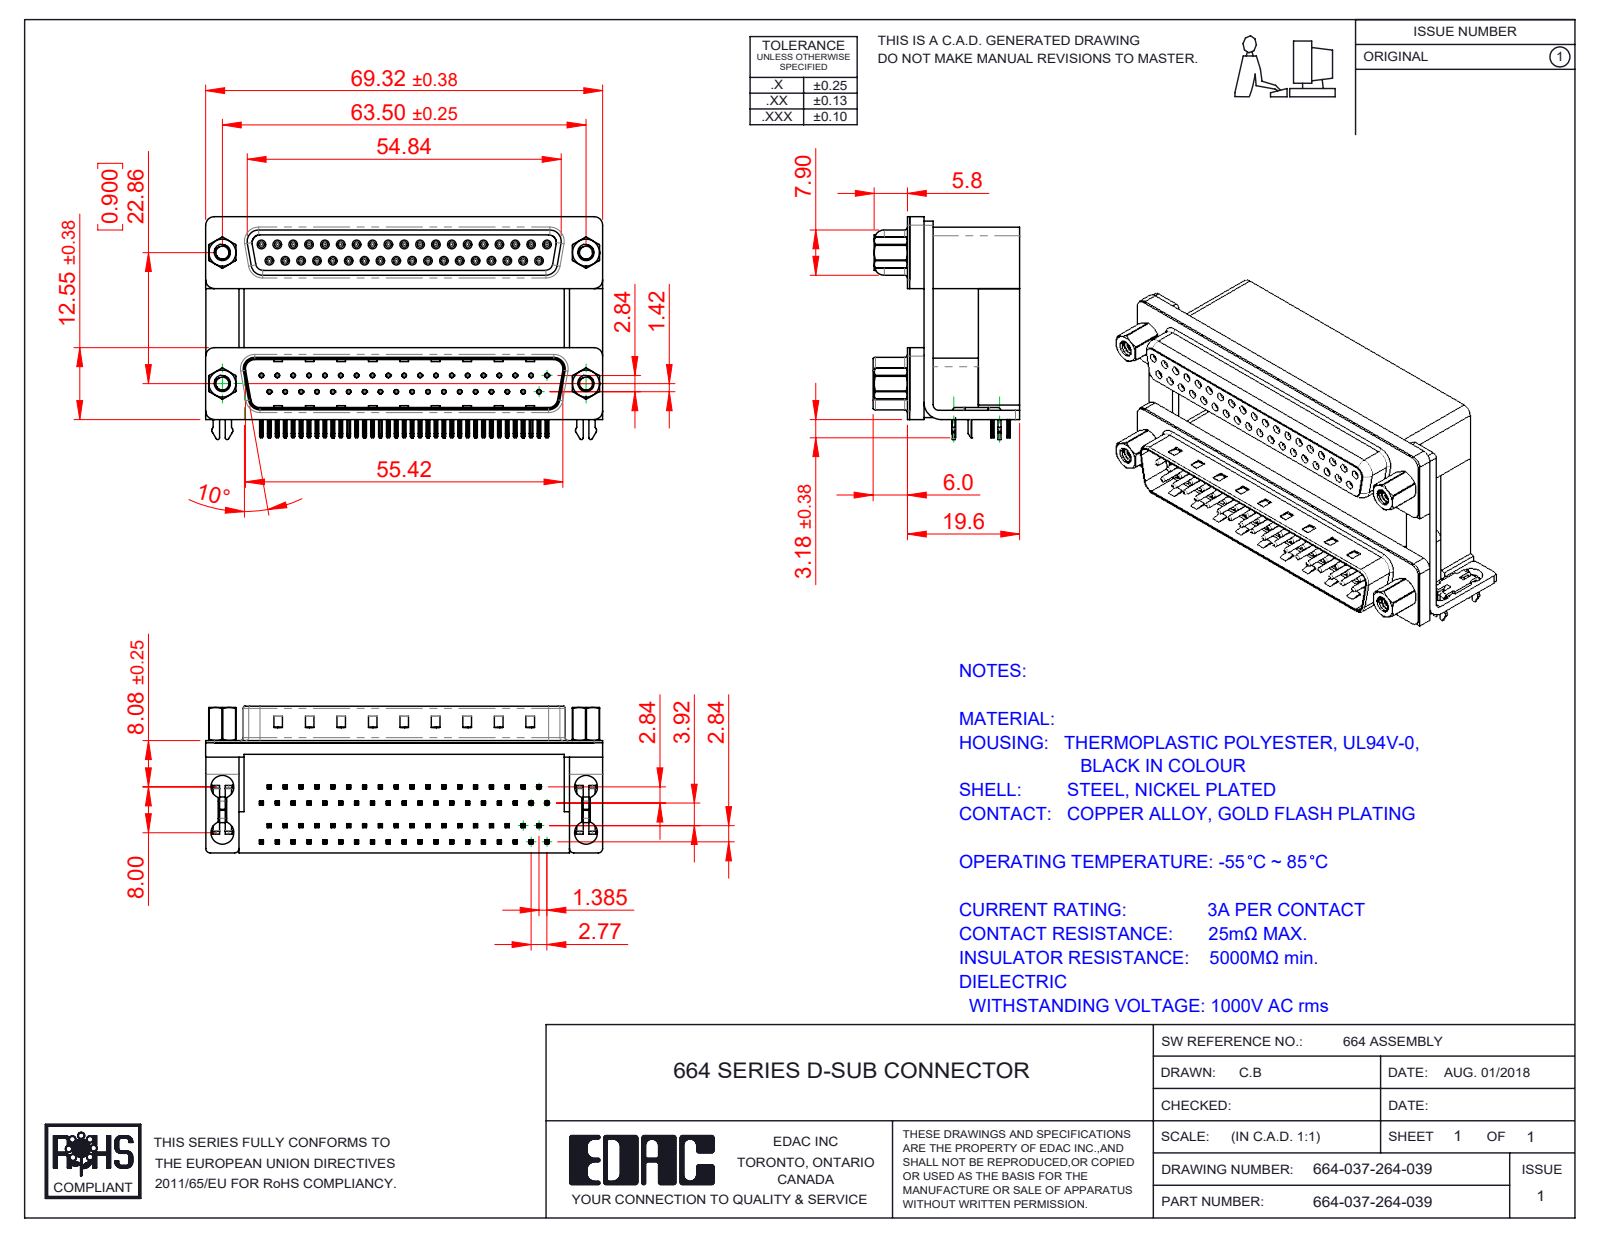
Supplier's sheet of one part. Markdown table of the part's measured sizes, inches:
| quantity | value |
| --- | --- |
| part name | 664 4-40 Hex Standoff 5; 664 Housing Lower_37 Contacts; 664 Shell Receptacle_37 Contacts; 664 Contact Top Lower (+8 more) |
| STEP written by | SolidWorks 2020 (CONFIG_CONTROL_DESIGN) |
| units | inches |
| bodies | 91 solids, 9349 faces (4887 planar, 2371 cylindrical, 2091 other) |
| overall size | 2.729 × 1.532 × 1.008 |
| volume | 2.021 in³ |
| surface area | 54.71 in² |
| round holes (diameter × count) | 0.031 × 74, 0.014 × 37, 0.035 × 37, 0.157 × 8, 0.089 × 4, 0.09 × 4, 0.138 × 4, 0.189 × 4, 0.197 × 4 |
| round bosses / shafts (diameter × count) | 0.047 × 37, 0.03 × 37, 0.193 × 4, 0.187 × 4, 0.154 × 4, 0.11 × 4 |
| partial cylindrical surfaces (radius × count) | 0.004 × 298, 0.01 × 158, 0.006 × 148, 0.005 × 74, 0.014 × 74, 0.013 × 37, 0.011 × 18, 0.02 × 16 |
| main face-to-face distances | 0.016, 0.756, 0.472, 0.283, 0.086, 0.112, 0.026, 0.886, 0.488, 0.421 |
| hole center spacings | 0.109, 0.218, 0.124, 0.327, 0.436, 0.545, 0.654, 0.763 |
